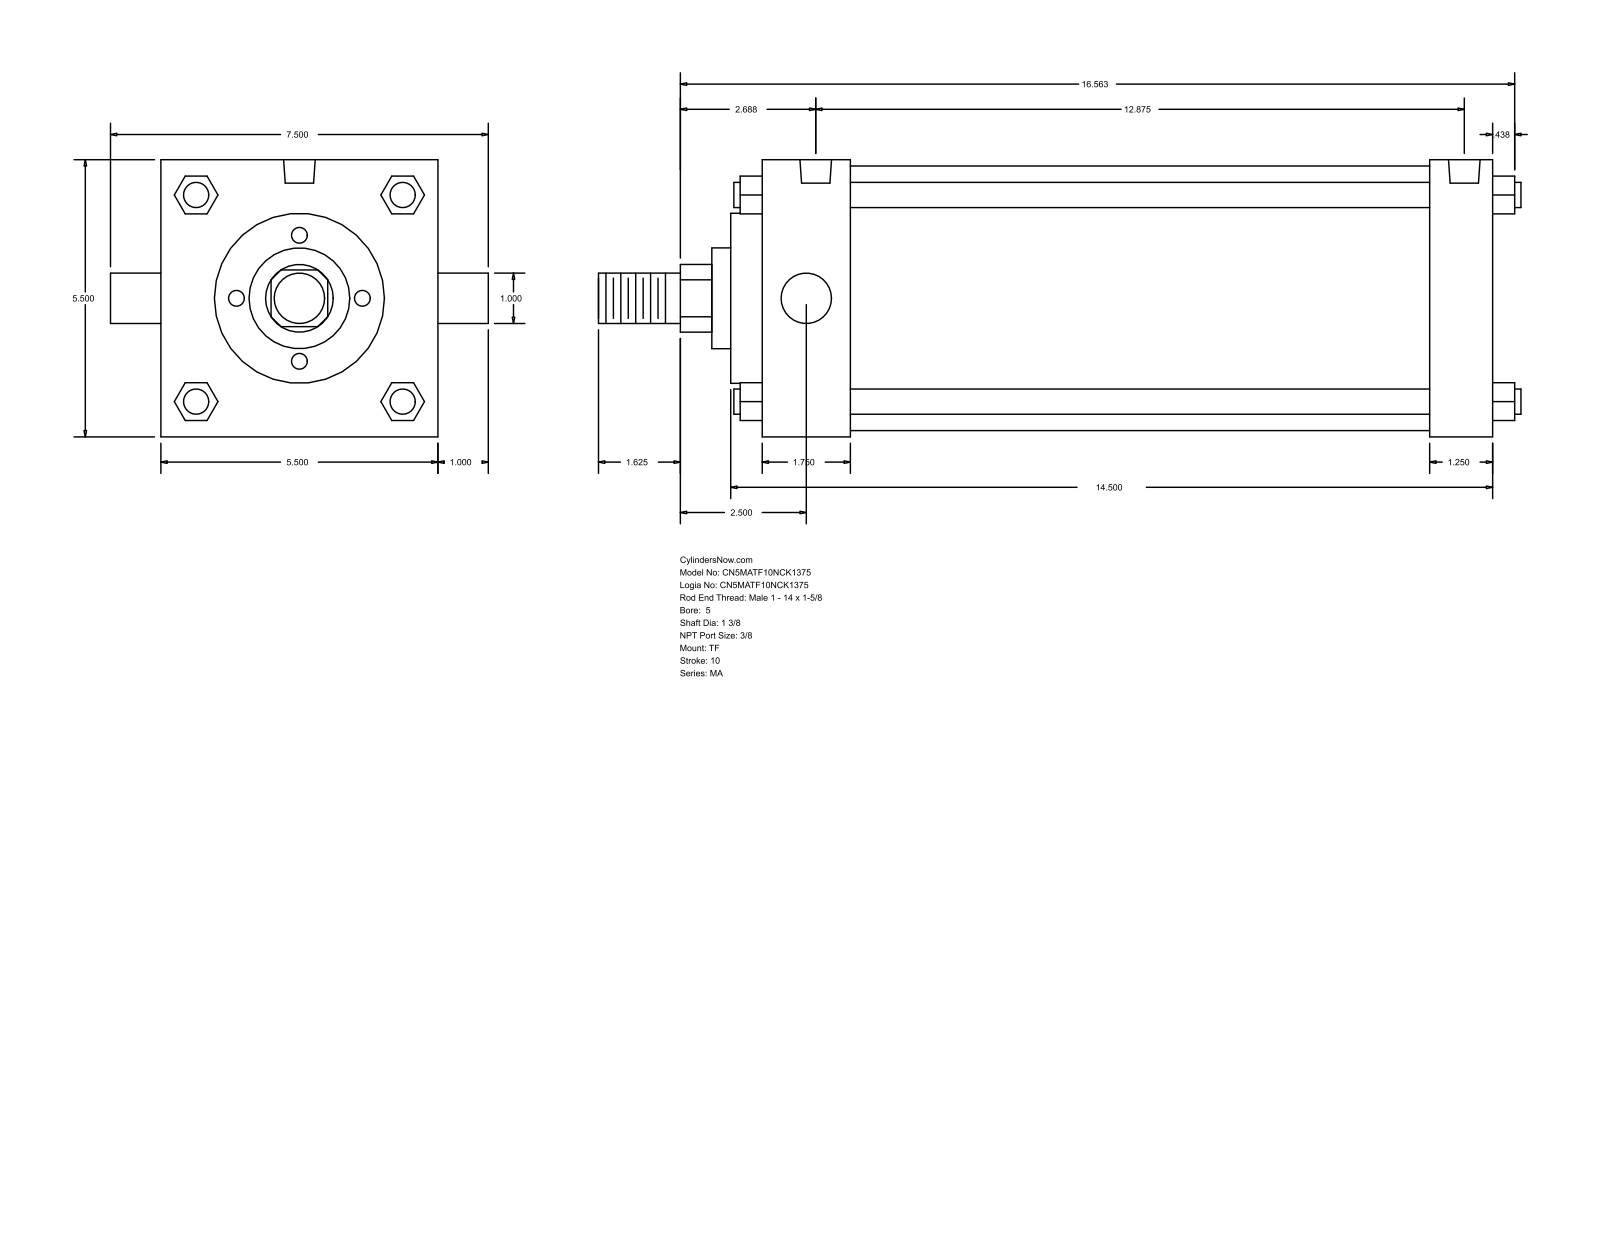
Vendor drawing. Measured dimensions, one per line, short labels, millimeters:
name: MA_TF__0500_1.375
written by: GSSL Pune (CONFIG_CONTROL_DESIGN)
unit: mm
bodies: 0 solids, 122 faces (93 planar, 29 cylindrical, 0 other)
size: 465.14 × 190.5 × 139.7
holes: 3× ⌀11.11, 2× ⌀15.93
bosses: 4× ⌀12.7, 2× ⌀25.4, 1× ⌀133.35, 1× ⌀85.72, 1× ⌀50.8, 1× ⌀34.92
rounds: 1× R17.06
face distances: 139.7, 368.3, 336.55, 31.75, 44.45, 292.1, 323.85, 15.87, 60.32, 352.42
hole spacings: 4.77, 322.26, 317.49, 327.03
